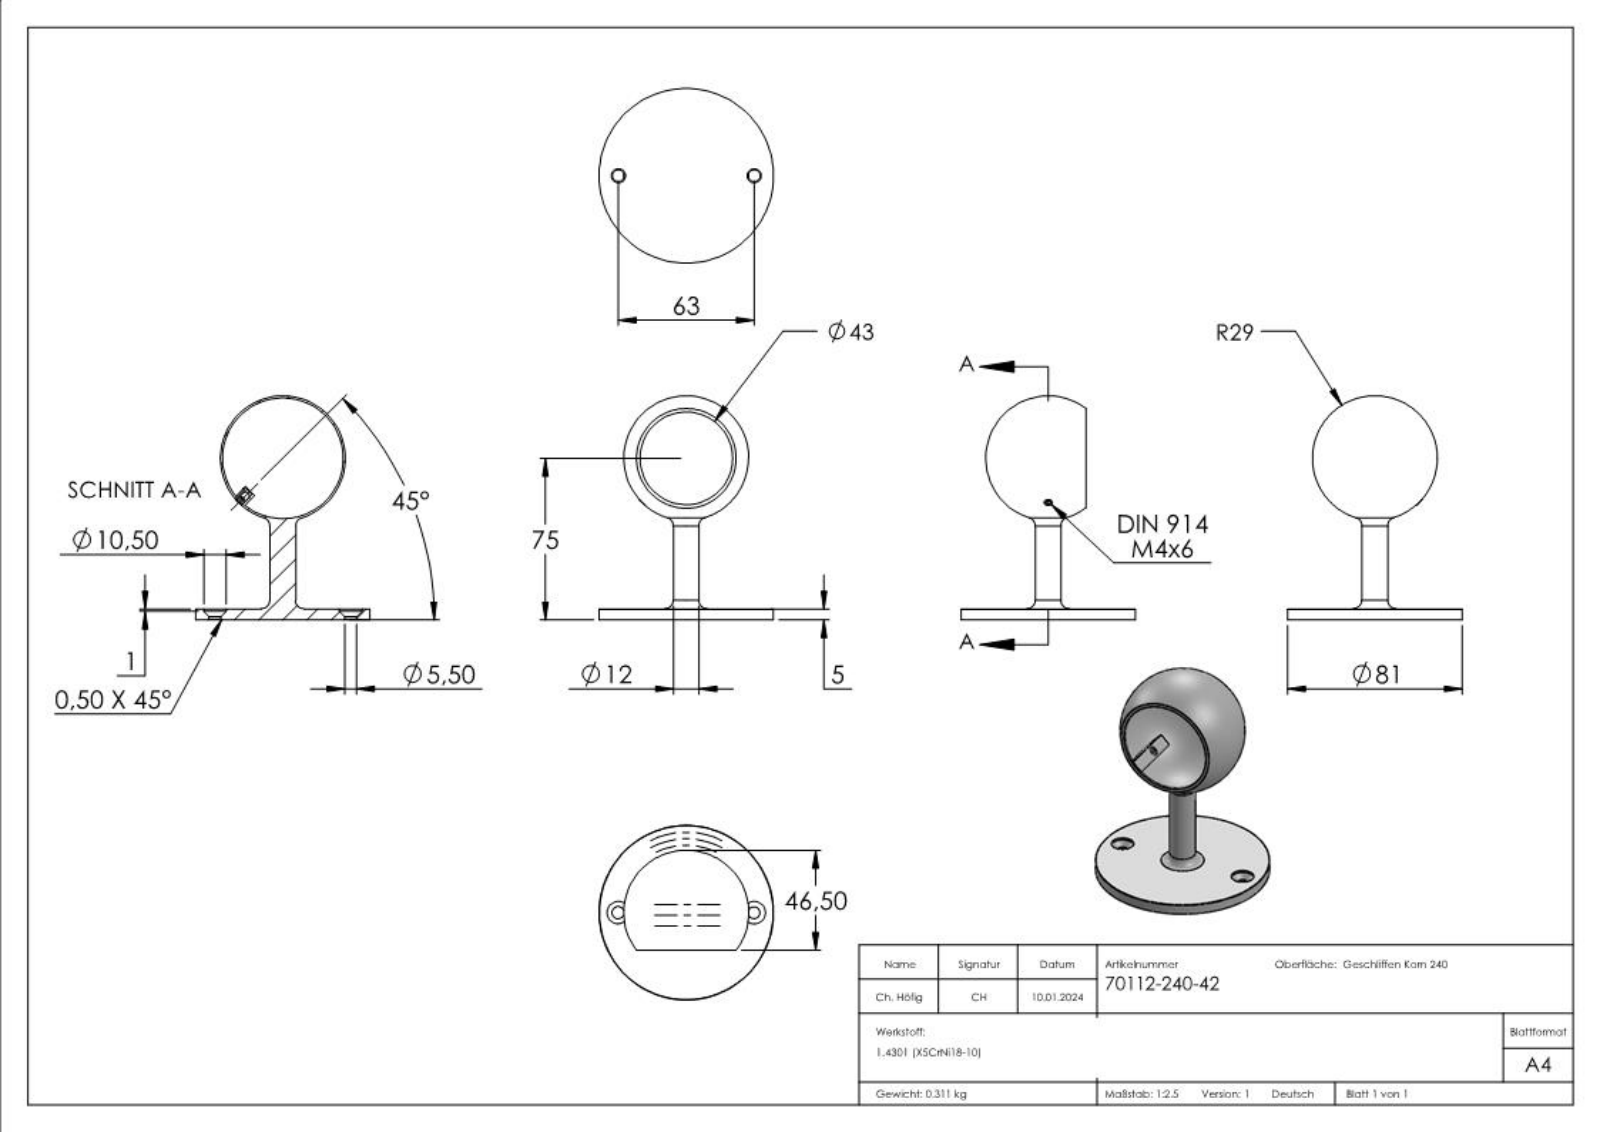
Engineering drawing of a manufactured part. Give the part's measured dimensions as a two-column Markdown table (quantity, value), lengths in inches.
| quantity | value |
| --- | --- |
| part name | 7011X-XX Konfig_70112-240-42; 70112-240-42; DIN913_DIN 913 M4x6 |
| STEP written by | SolidWorks 2018 (CONFIG_CONTROL_DESIGN) |
| units | inches |
| bodies | 2 solids, 280 faces (173 planar, 9 cylindrical, 98 other) |
| overall size | 4.094 × 3.189 × 3.189 |
| volume | 2.401 in³ |
| surface area | 46.74 in² |
| round holes (diameter × count) | 0.217 × 2, 0.413 × 2, 0.13 × 1, 1.693 × 1 |
| round bosses / shafts (diameter × count) | 3.189 × 1, 0.472 × 1, 0.157 × 1 |
| main face-to-face distances | 0.197, 0.039, 0.236, 1.102, 1.142, 0.079, 0.059, 0.492, 0.61, 0.65 |
| hole center spacings | 2.48 |
